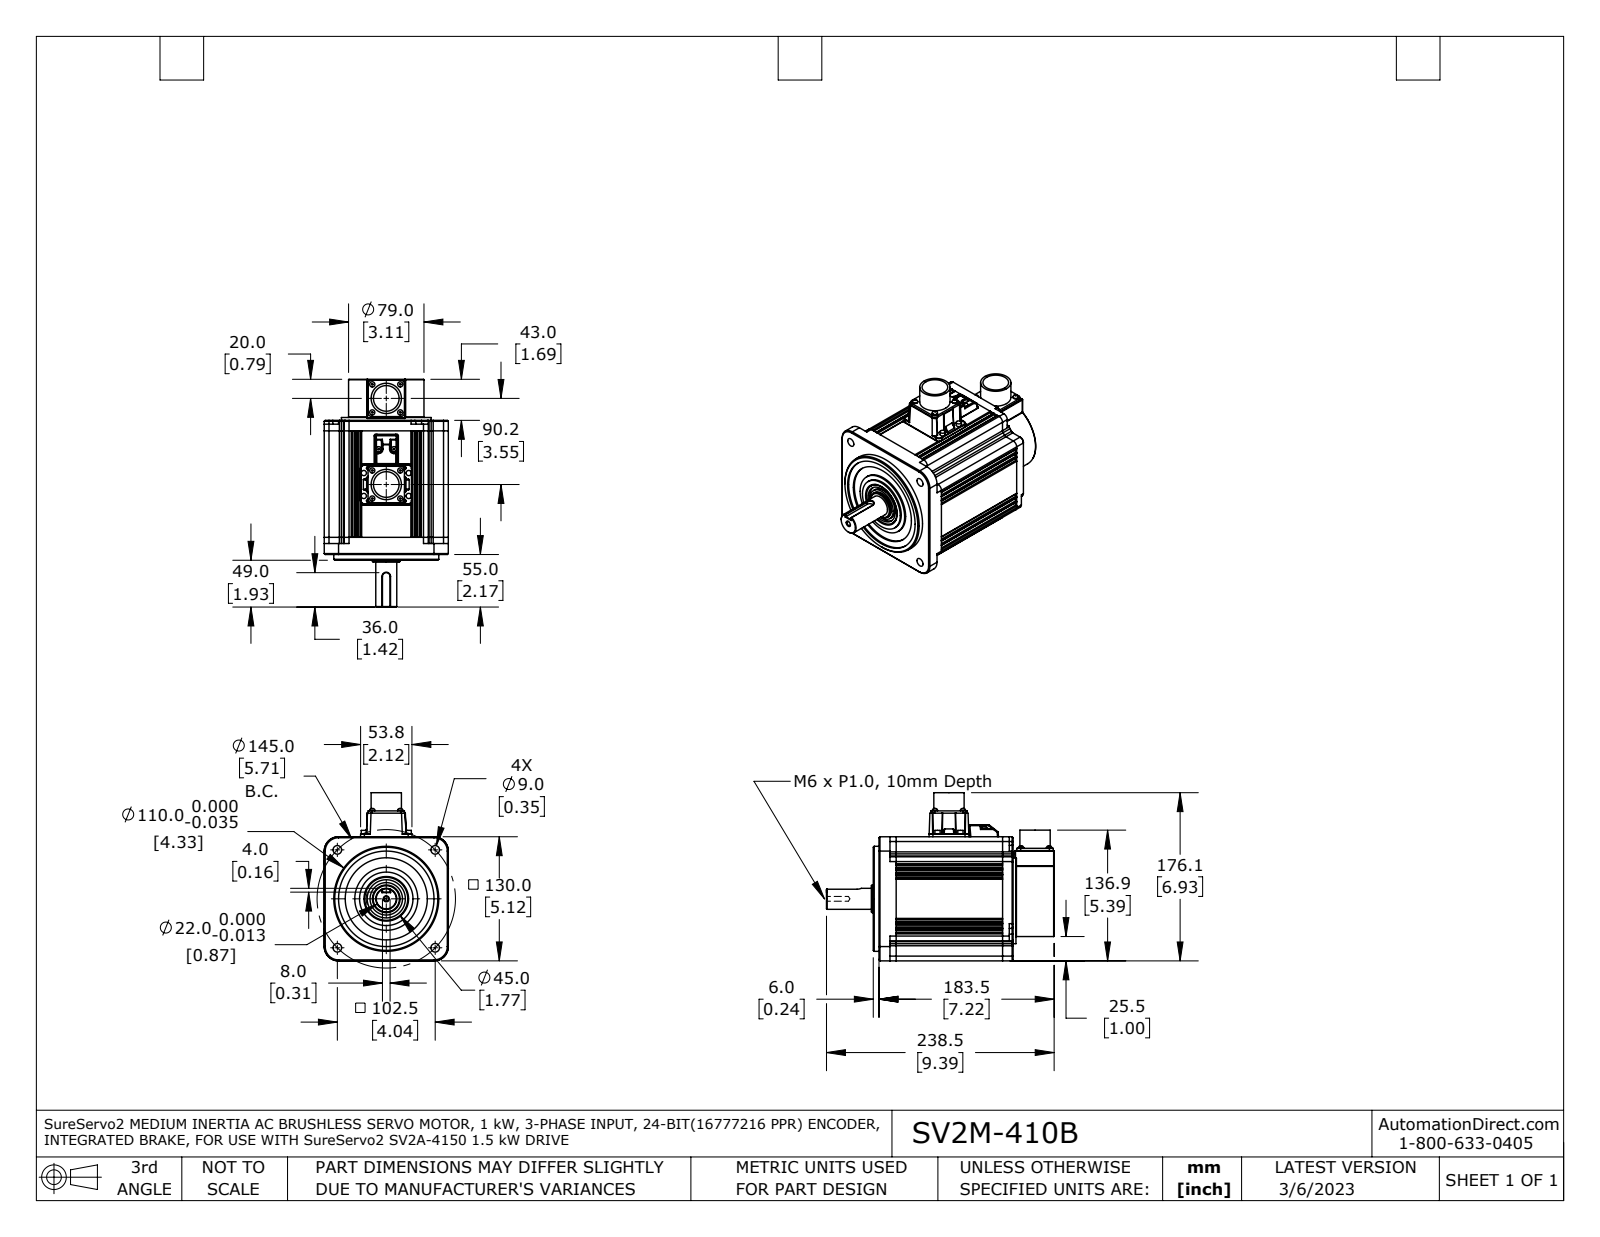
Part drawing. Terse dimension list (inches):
name: SV2M-x10B fxt
written by: SolidWorks 2021 (AUTOMOTIVE_DESIGN)
unit: in
bodies: 2 solids, 699 faces (305 planar, 236 cylindrical, 158 other)
size: 9.39 × 6.935 × 5.118
volume: 150.7 in³; area: 245.9 in²
holes: 4× ⌀0.354, 2× ⌀1.058, 1× ⌀0.197, 1× ⌀1.142, 1× ⌀1.575, 1× ⌀1.772, 1× ⌀3.386, 1× ⌀3.937
bosses: 8× ⌀0.217, 6× ⌀0.213, 2× ⌀1.25, 1× ⌀4.331, 1× ⌀3.701, 1× ⌀3.11, 1× ⌀2.598, 1× ⌀2.205
rounds: 87× R0.039, 24× R0.02, 17× R0.157, 8× R0.118, 8× R0.197, 2× R0.079
face distances: 0.827, 4.291, 5.118, 2.402, 5.531, 0.118, 0.211, 0.959, 1.693, 7.224
hole spacings: 2.855, 4.037, 5.709, 3.55
